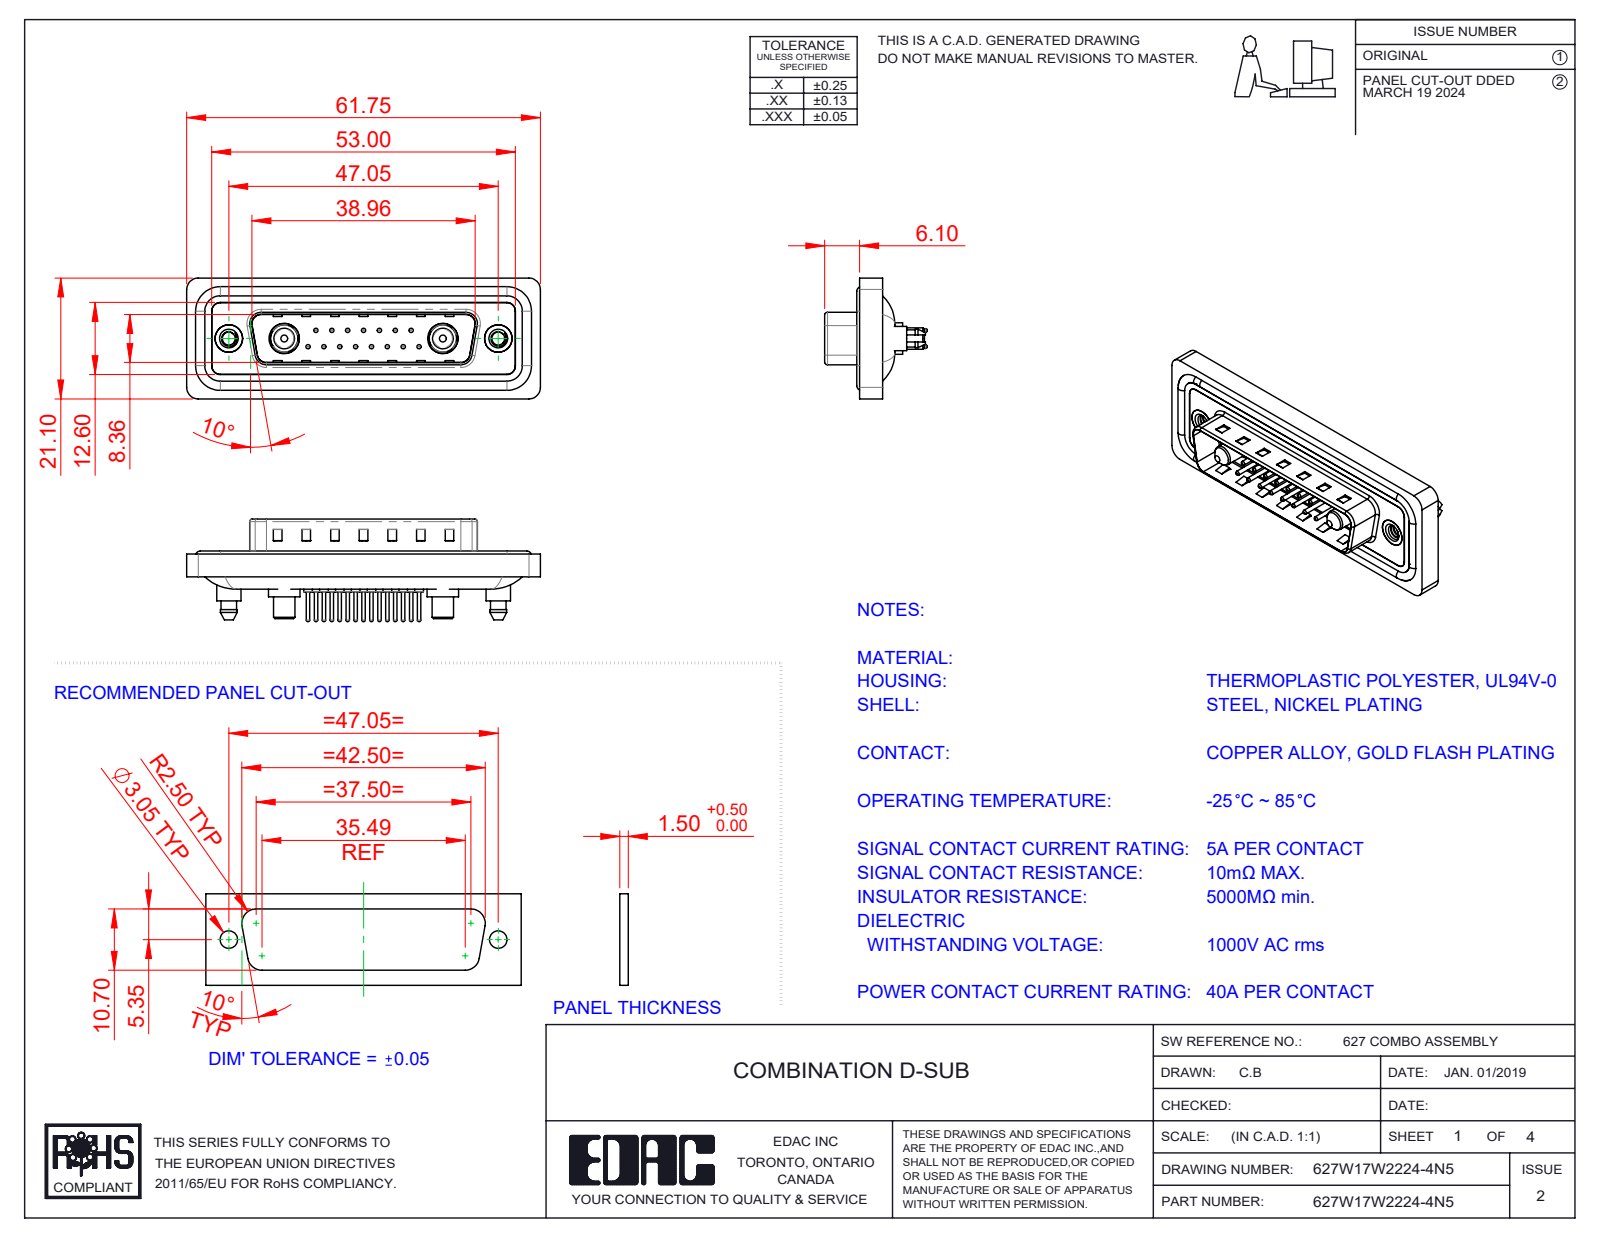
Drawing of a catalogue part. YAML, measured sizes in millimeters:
part_name: "627Combo Shell Rear_25 Contacts; 627Combo Housing_17W2; 627Combo Contact Row 1_24; 627Combo Contact Row 2_24 (+5 more)"
step_written_by: "SolidWorks 2023 (CONFIG_CONTROL_DESIGN)"
units: millimeters
bodies: {solids: 26, faces: 1166, planar: 350, cylindrical: 468, other: 348}
overall_size: [61.75, 21.1, 17.9]
volume: 7437
surface_area: 12269
round_holes:
  - {diameter: 0.75, count: 15}
  - {diameter: 1.6, count: 15}
  - {diameter: 2, count: 15}
  - {diameter: 2.26, count: 2}
  - {diameter: 4, count: 2}
  - {diameter: 4.8, count: 2}
  - {diameter: 4.85, count: 2}
  - {diameter: 5, count: 2}
  - {diameter: 5.3, count: 2}
round_bosses_or_shafts:
  - {diameter: 1.5, count: 15}
  - {diameter: 0.6, count: 15}
  - {diameter: 1.6, count: 4}
  - {diameter: 5.5, count: 2}
  - {diameter: 5.4, count: 2}
  - {diameter: 5.2, count: 2}
  - {diameter: 4.9, count: 2}
  - {diameter: 4.75, count: 2}
partial_cylinders:
  - {radius: 1.5, count: 24}
  - {radius: 2, count: 18}
  - {radius: 1.6, count: 10}
  - {radius: 0.5, count: 8}
  - {radius: 0.25, count: 4}
  - {radius: 0.6, count: 4}
  - {radius: 0.65, count: 4}
  - {radius: 0.9, count: 4}
face_to_face_distances: [0.4, 1.5, 1.1, 1.6, 0.5, 3.1, 2.9, 0.82, 9.58, 4.1]
hole_center_spacings: [3.16, 2.77, 5.54, 8.31, 5.04, 7.49, 11.08, 5.03]
